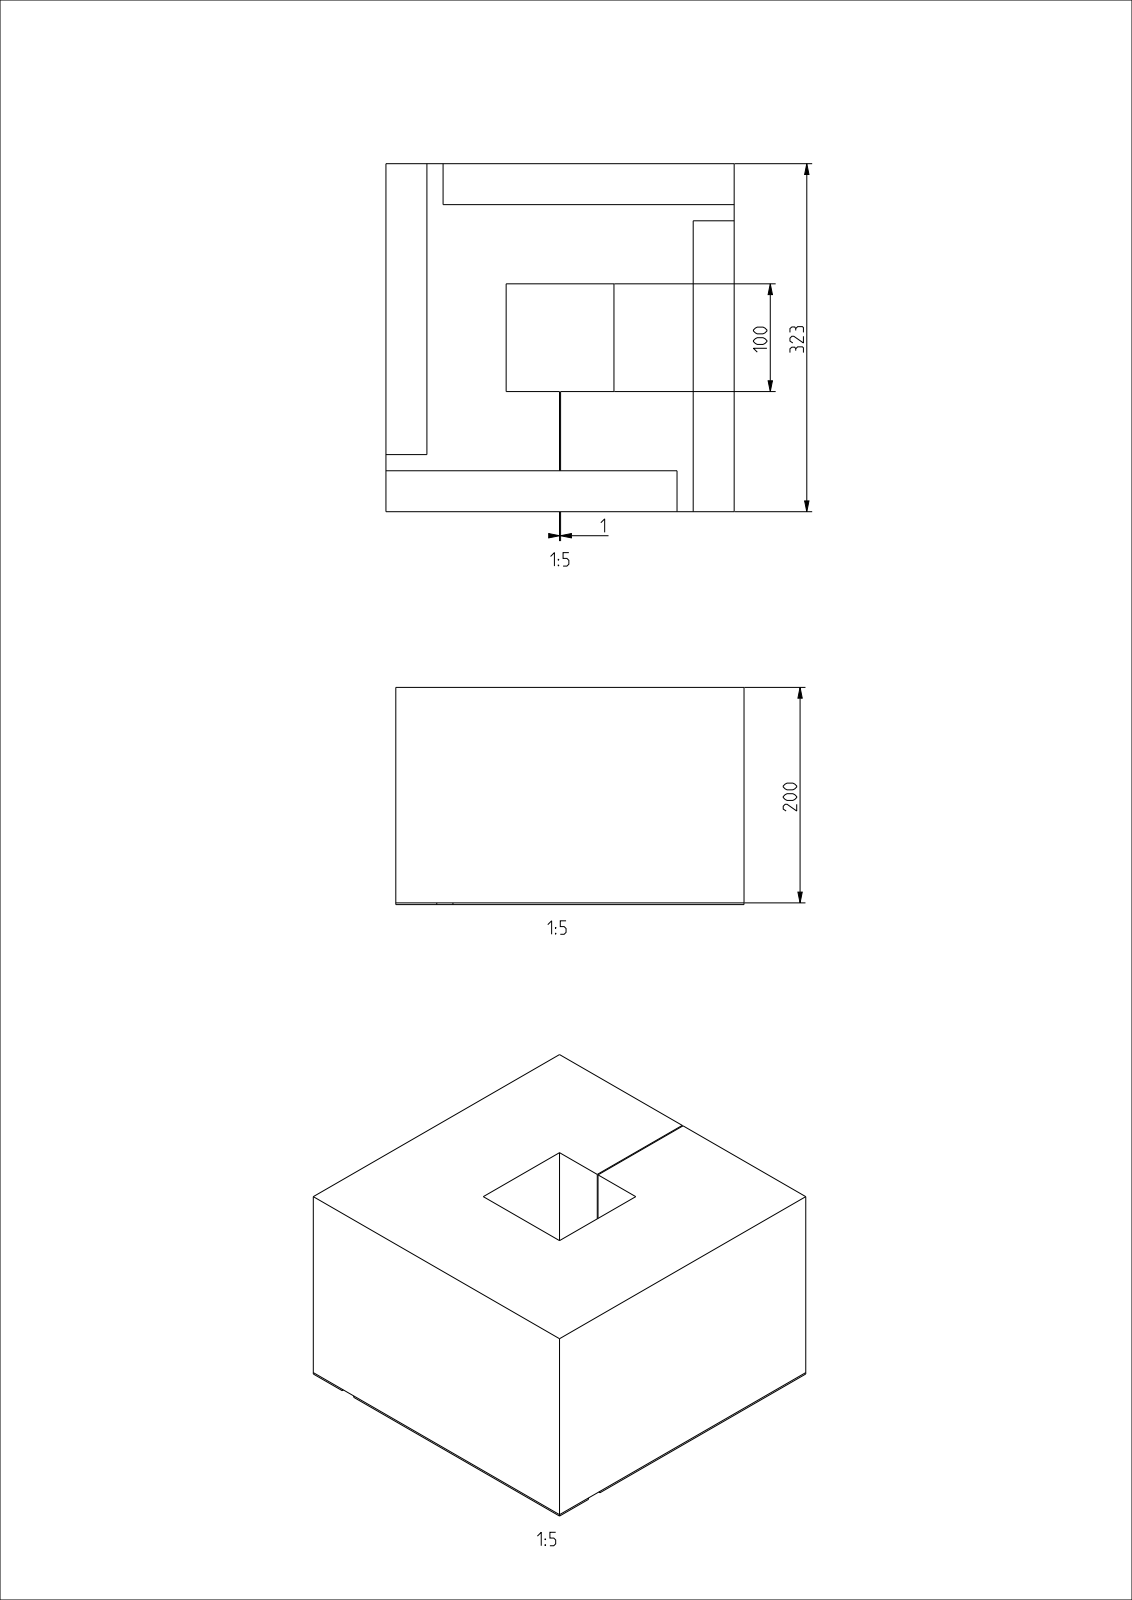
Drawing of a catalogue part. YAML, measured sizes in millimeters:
part_name: "T-00952; T-01465_AF0; T-01464_ASM"
step_written_by: "CREO PARAMETRIC BY PTC INC, 2022281 (AUTOMOTIVE_DESIGN)"
units: millimeters
bodies: {solids: 5, faces: 38, planar: 38, cylindrical: 0, other: 0}
overall_size: [323, 323, 201.6]
volume: 18910000
surface_area: 657057
face_to_face_distances: [323, 200, 111.5, 211.5, 161, 162, 1.6, 201.6, 49.5, 50.5]
